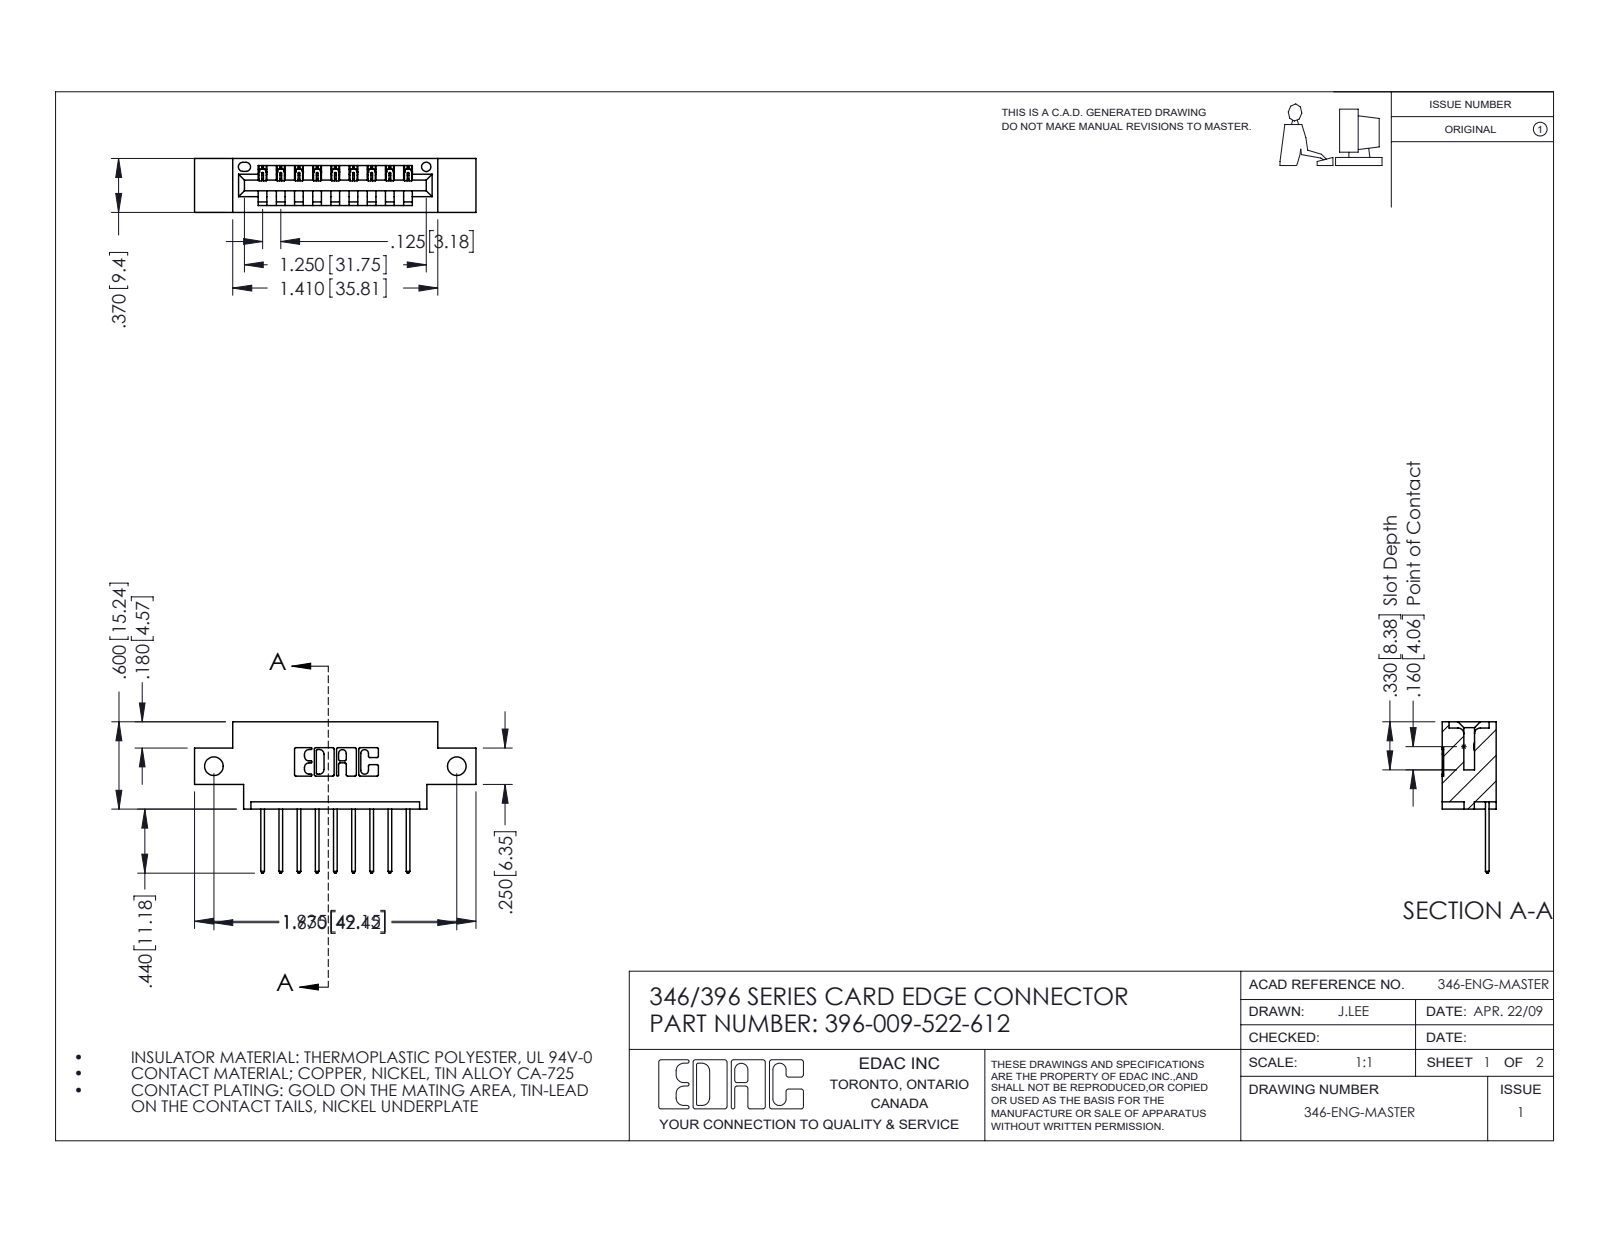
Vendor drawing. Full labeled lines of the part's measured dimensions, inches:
Part name (STEP PRODUCT): 345-292-001_345-293-122; 396-009-522-612; 346 Part_0.170 Offset - Side Mount
STEP written by: SolidWorks 2016 (CONFIG_CONTROL_DESIGN)
Units: inches
Bodies: 10 solids, 648 faces (440 planar, 208 cylindrical, 0 other)
Overall size (bounding box): 1.935 × 1.04 × 0.37
Volume: 0.259 in³ · Surface area: 7.729 in²
Round holes (diameter × count): ⌀0.128 ×2, ⌀0.064 ×1
Partial cylindrical surfaces — rounded edges, fillets, slot ends (radius × count): R0.01 ×22, R0.006 ×18, R0.01 ×18, R0.007 ×6, R0.031 ×6, R0.026 ×3, R0.031 ×2, R0.04 ×2
Main face-to-face distances: 0.25, 0.37, 0.048, 0.322, 0.072, 0.298, 0.025, 0.148, 0.222, 0.1
Hole centre spacings: 1.67
